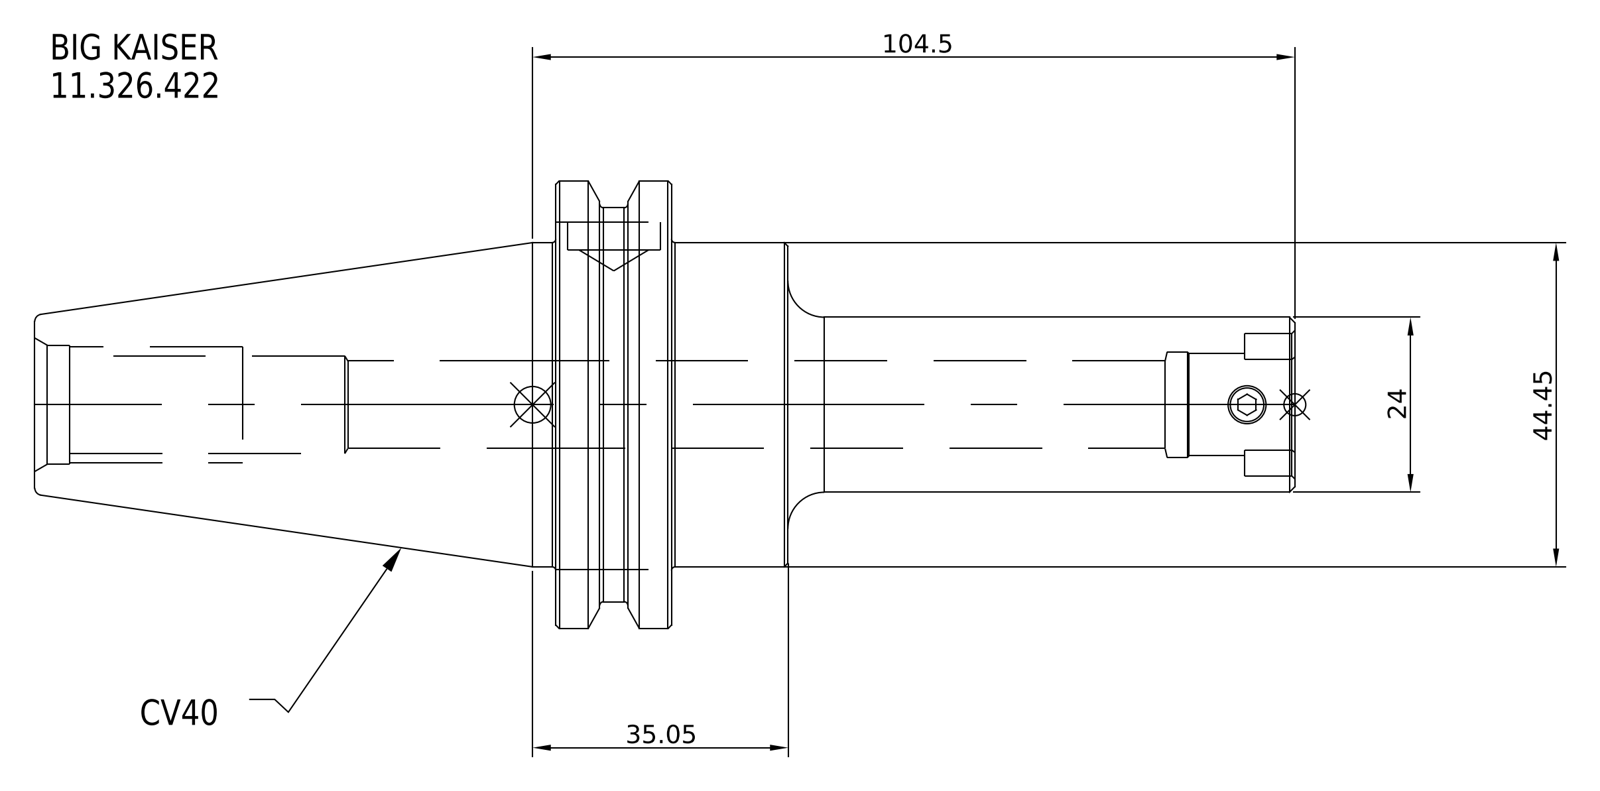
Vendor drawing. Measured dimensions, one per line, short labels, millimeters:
name: 11_326_422
written by: SolidWorks 2021 (CONFIG_CONTROL_DESIGN)
unit: mm
bodies: 1 solid, 27 faces (7 planar, 12 cylindrical, 8 other)
size: 172.75 × 63.5 × 63.5
volume: 174 004 mm³; area: 24 444 mm²
bosses: 1× ⌀63.5, 1× ⌀56.36, 1× ⌀44.45, 1× ⌀24
face distances: 15.88, 16, 31.88, 103.3, 87.3, 71.42, 69.45, 85.45, 101.33, 172.75
